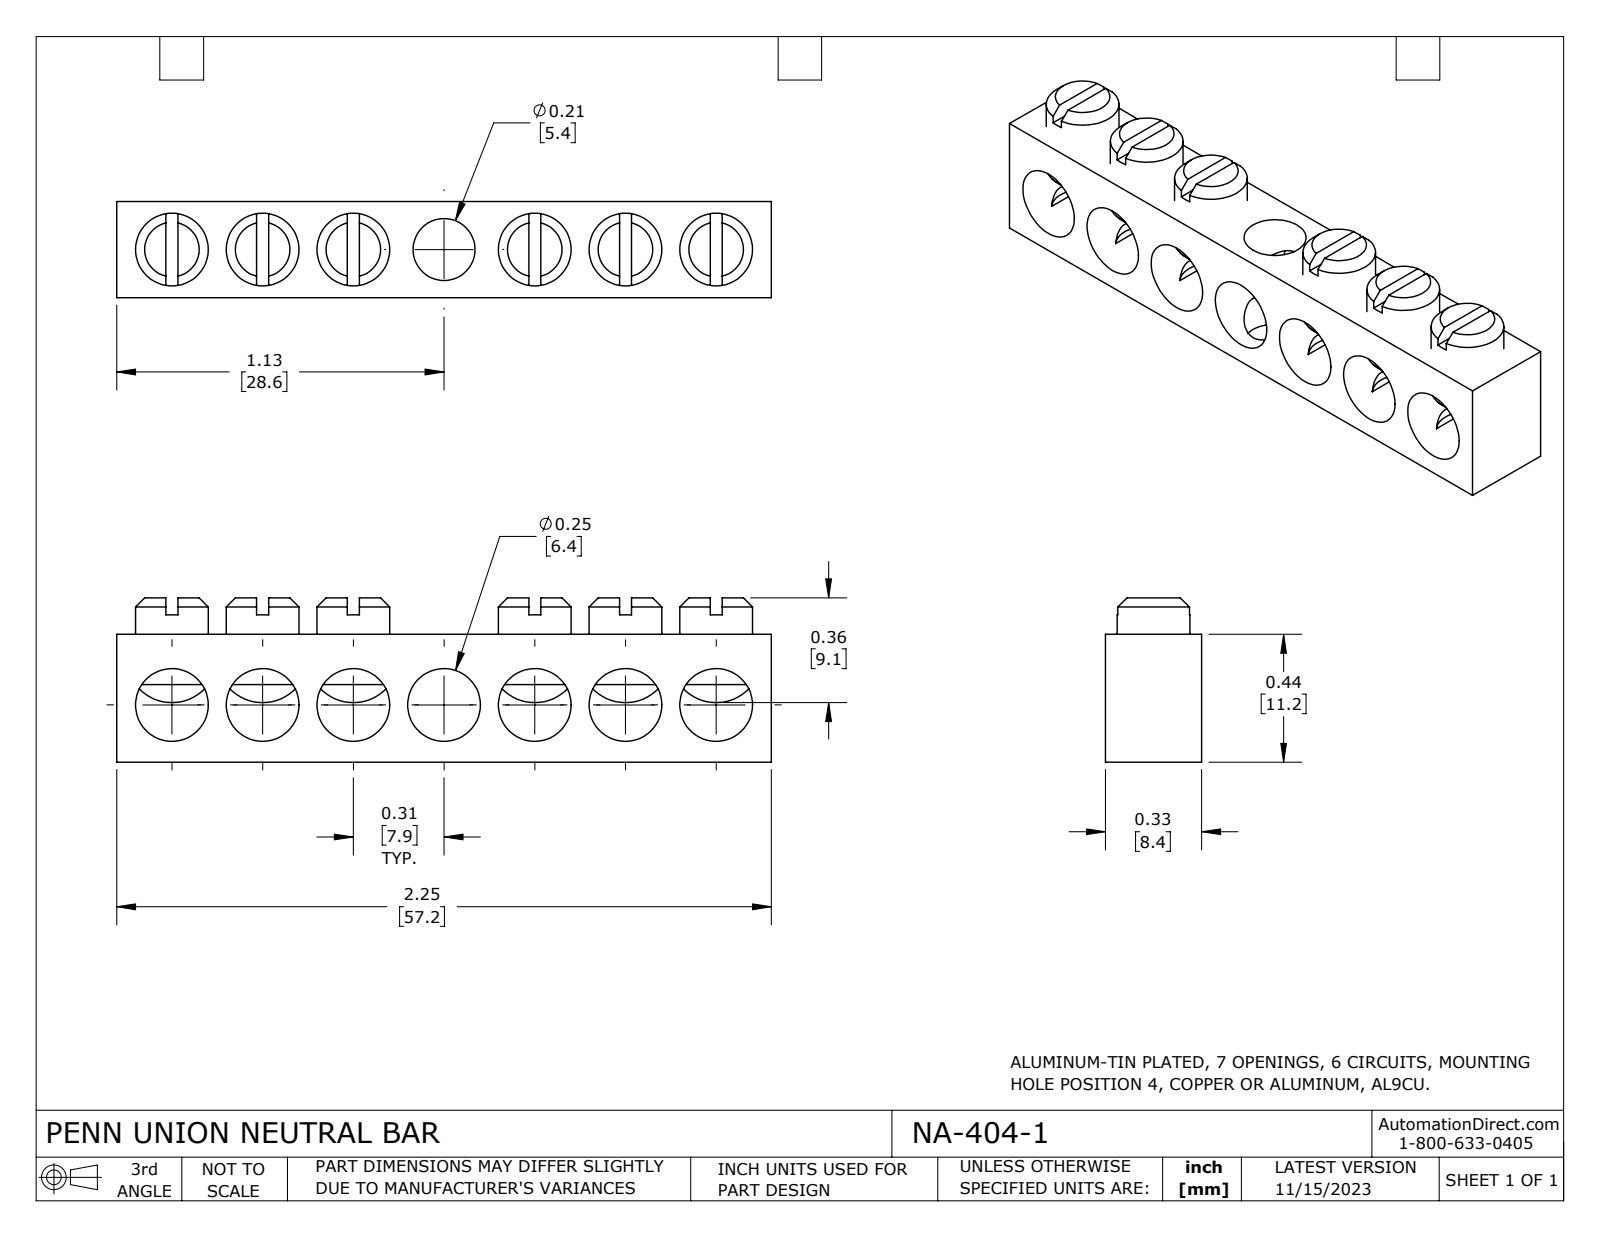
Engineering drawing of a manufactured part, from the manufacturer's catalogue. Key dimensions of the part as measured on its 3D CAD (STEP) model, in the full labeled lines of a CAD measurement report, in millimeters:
Part name (STEP PRODUCT): NA-404-1
STEP written by: SolidWorks 2023 (CONFIG_CONTROL_DESIGN)
Units: millimetres
Bodies: 7 solids, 132 faces (48 planar, 54 cylindrical, 30 other)
Overall size (bounding box): 57.2 × 14.4 × 8.4
Volume: 4 420 mm³ · Surface area: 4 621 mm²
Round holes (diameter × count): ⌀5.4 ×7, ⌀6.4 ×7
Round bosses / shafts (diameter × count): ⌀6.4 ×6
Main face-to-face distances: 8.4, 11.2, 57.2, 14.4, 3.2, 7.9, 15.8, 31.7, 1, 12.9
Hole centre spacings: 7.9, 15.8, 23.7, 31.7, 39.6, 47.5
